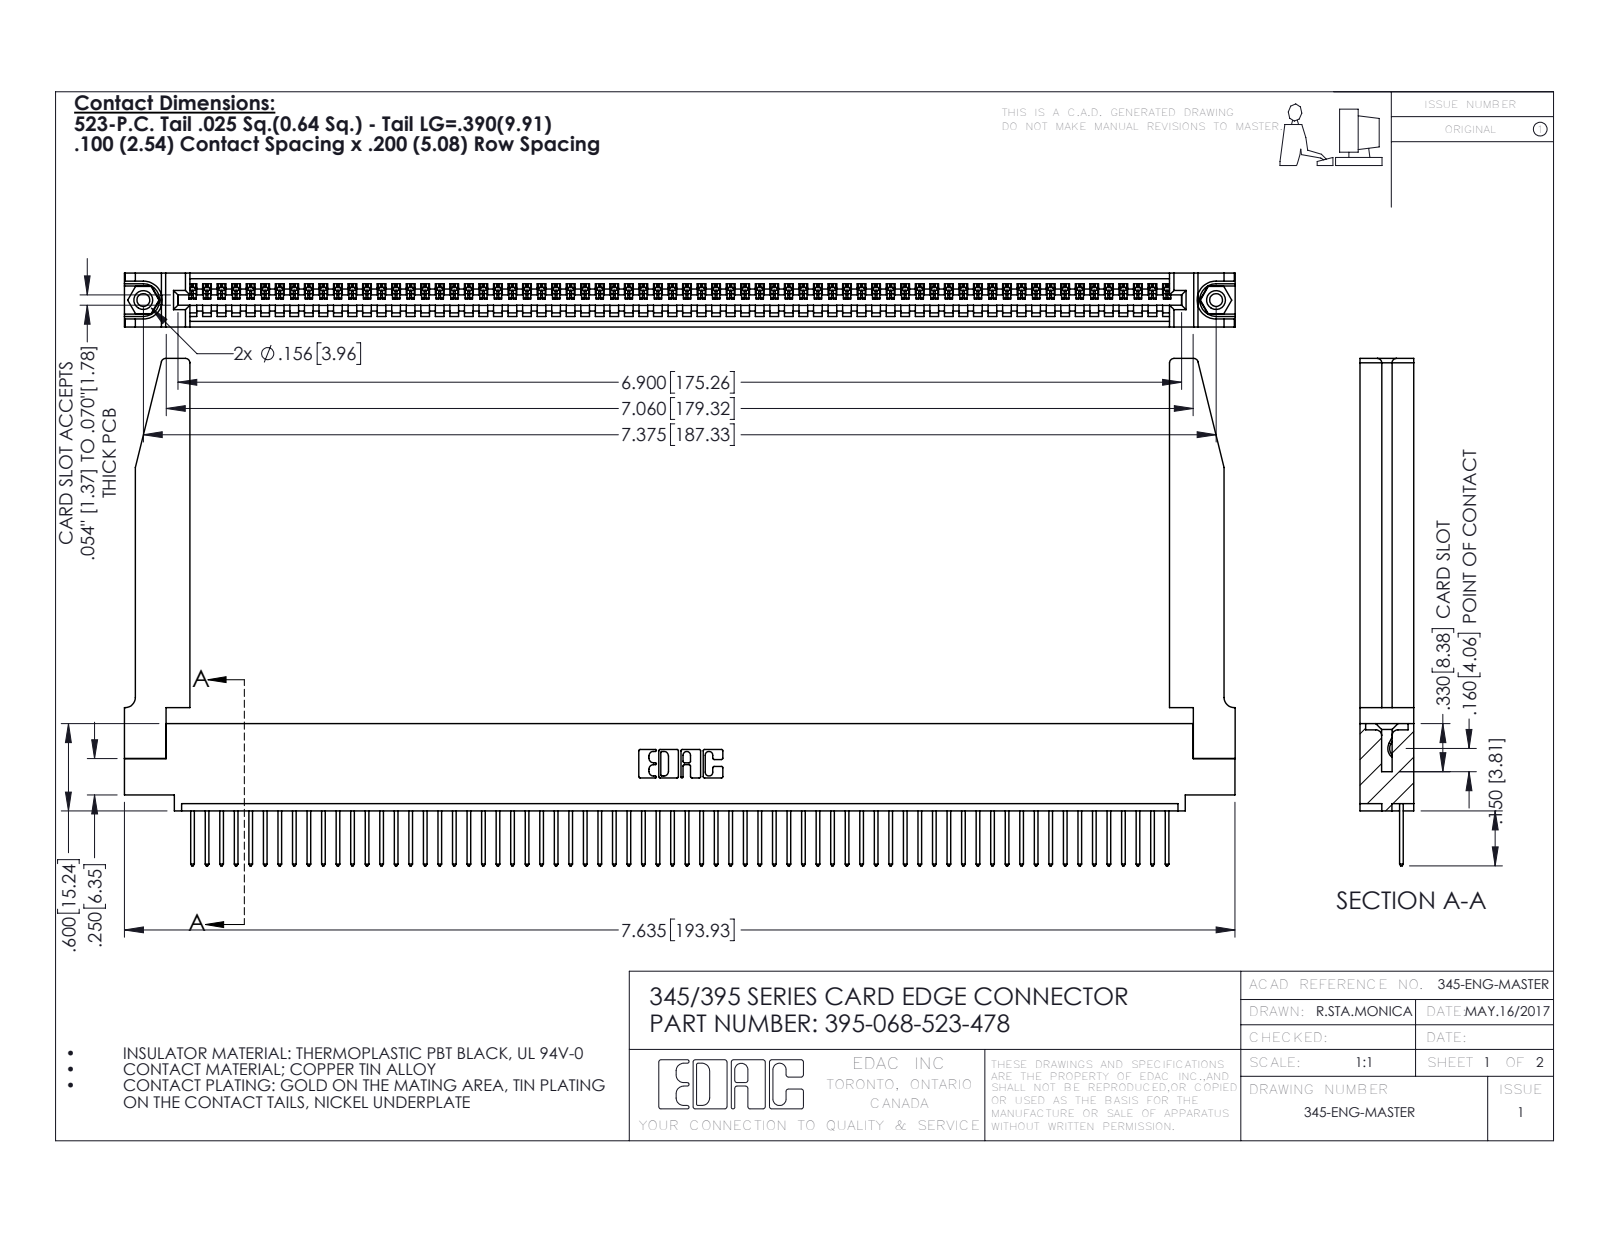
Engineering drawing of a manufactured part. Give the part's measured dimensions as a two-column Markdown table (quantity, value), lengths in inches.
| quantity | value |
| --- | --- |
| part name | 345-292-001_345-293-123; 345 Part_0.110 Offset - 0.156 Dia-TH; 345-250-001_345-250-001-102; 395-068-523-478 (+1 more) |
| STEP written by | SolidWorks 2016 (CONFIG_CONTROL_DESIGN) |
| units | inches |
| bodies | 73 solids, 4308 faces (2946 planar, 1310 cylindrical, 52 other) |
| overall size | 7.636 × 3.487 × 0.37 |
| volume | 1.605 in³ |
| surface area | 49.58 in² |
| round holes (diameter × count) | 0.089 × 2, 0.125 × 2, 0.156 × 2, 0.064 × 1 |
| round bosses / shafts (diameter × count) | 0.155 × 2 |
| partial cylindrical surfaces (radius × count) | 0.006 × 136, 0.01 × 136, 0.01 × 22, 0.03 × 8, 0.007 × 6, 0.031 × 6, 0.026 × 3, 0.031 × 2 |
| main face-to-face distances | 0.072, 0.298, 0.37, 0.098, 0.272, 0.025, 0.2, 0.225, 0.149, 0.148 |
| hole center spacings | 0.27, 7.139, 7.375 |
